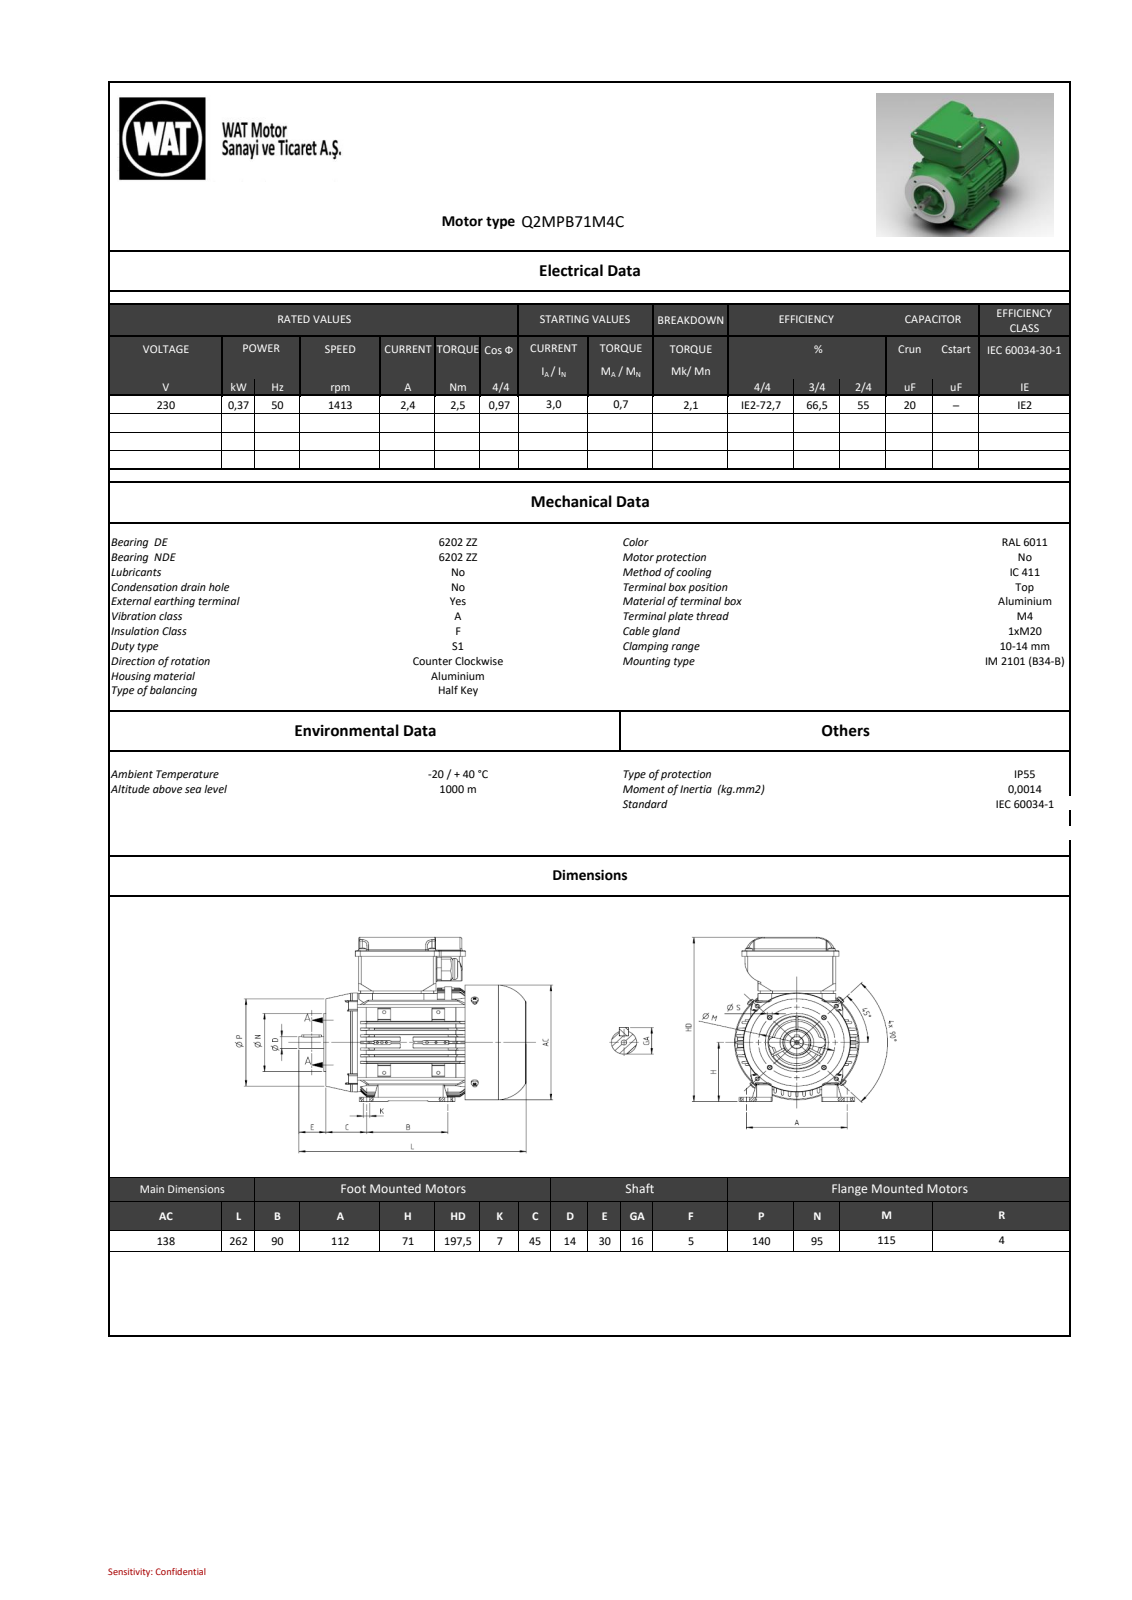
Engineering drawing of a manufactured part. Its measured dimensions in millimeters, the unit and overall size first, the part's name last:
Units: millimetres
Overall size (bounding box): 262 × 197.5 × 140.48
Round holes (diameter × count): ⌀3.65 ×8, ⌀4 ×8, ⌀4.5 ×8, ⌀2.5 ×6, ⌀3.3 ×5, ⌀8 ×5, ⌀4.65 ×4, ⌀4.8 ×4, ⌀5.2 ×4, ⌀7 ×4, ⌀3 ×3, ⌀3.7 ×3
Round bosses / shafts (diameter × count): ⌀8 ×8, ⌀4 ×8, ⌀3 ×8, ⌀3.3 ×4, ⌀140.48 ×1, ⌀138 ×1, ⌀115 ×1, ⌀95 ×1
Partial cylindrical surfaces — rounded edges, fillets, slot ends (radius × count): R1 ×133, R2 ×75, R0.5 ×38, R1.2 ×36, R5 ×18, R10 ×16, R2.5 ×14, R0.3 ×12
Main face-to-face distances: 3, 194.5, 197.5, 158.5, 1, 4, 5, 6.9, 32.1, 36
Hole centre spacings: 84.39, 84.47, 87.43, 55, 36.59, 60, 4.27, 4.37
Volume: 859 134 mm³ · Surface area: 510 822 mm²
Bodies: 26 solids, 2709 faces (1298 planar, 771 cylindrical, 640 other)
Part name (STEP PRODUCT): BY6434017xx_004-TK_QM63-80; BY6424130xx_004-TKK_QM63-80; BY6422457xx_005-MOTOR_KAPAGI_QS71FB_ISLEME; 641304741_AZ-KAMA PARALEL A 5x5x22 St50 DIN6885 (+8 more)
STEP written by: SIEMENS PLM Software NX2206.8101 (AUTOMOTIVE_DESIGN)
